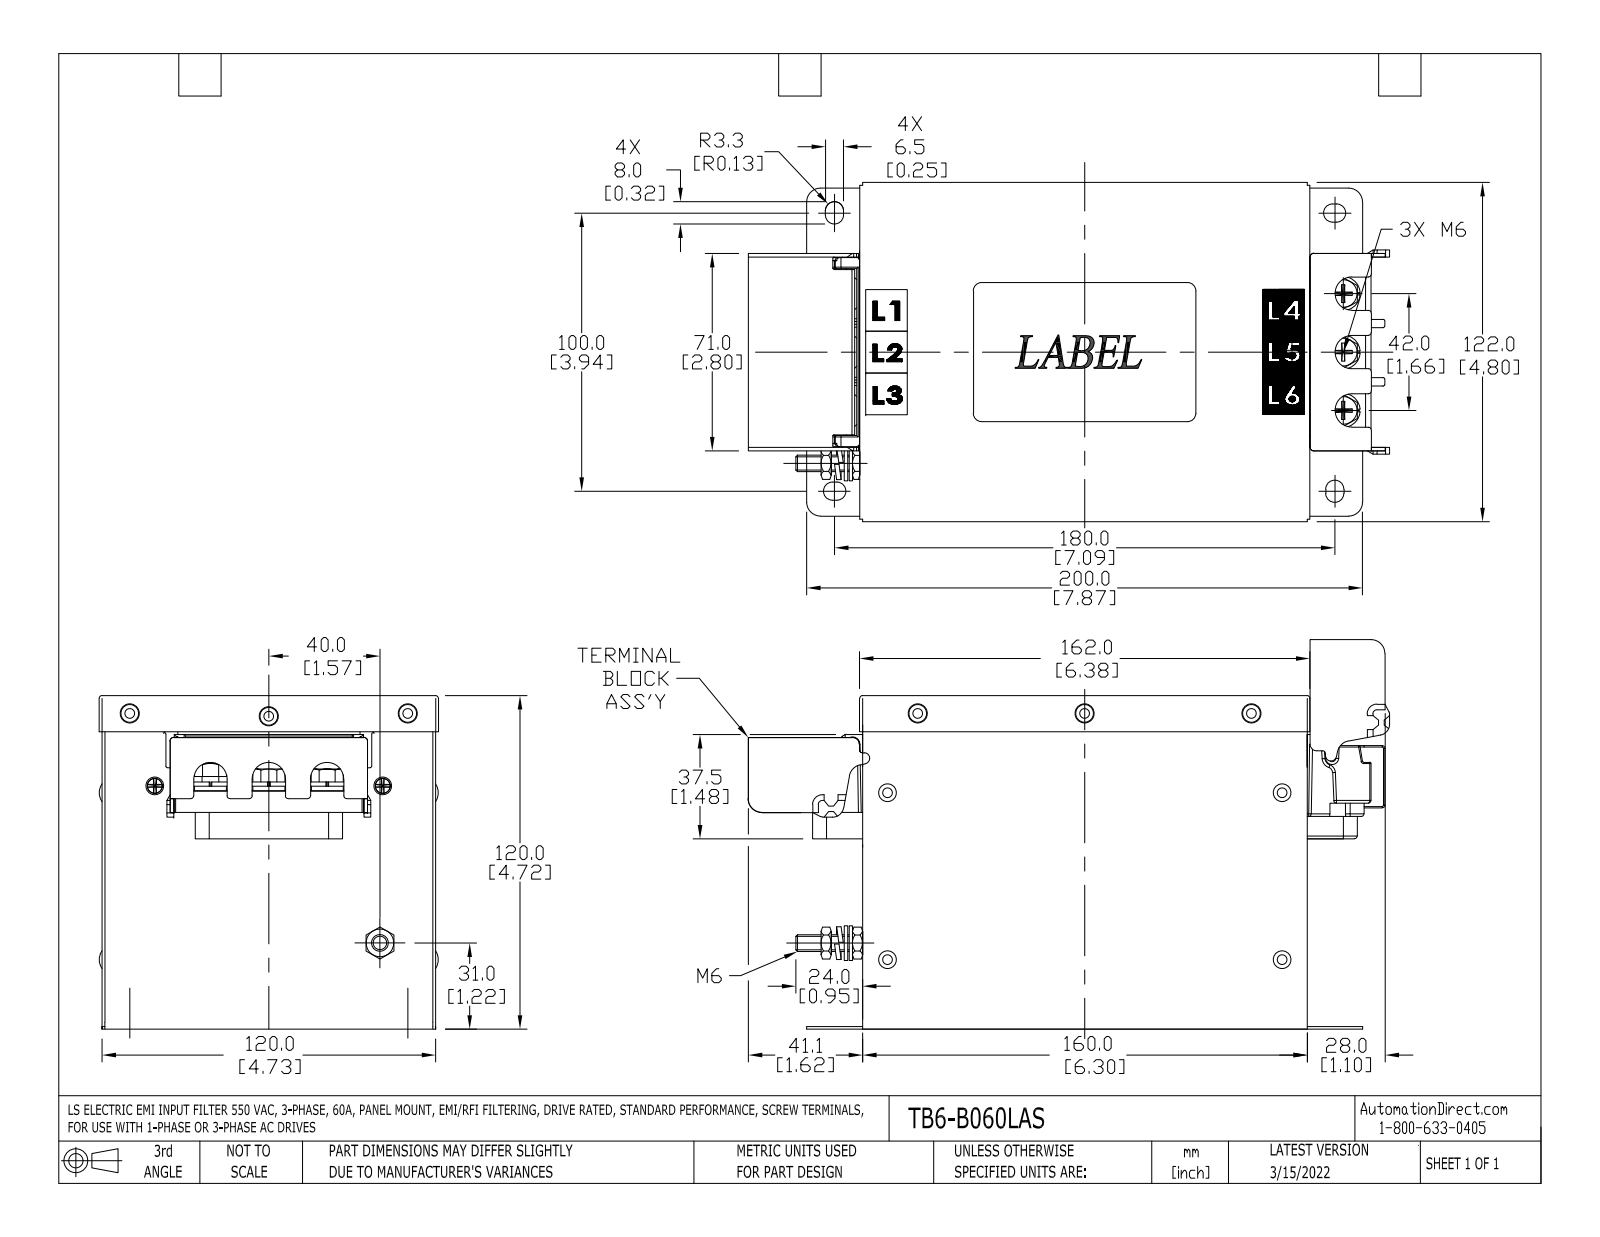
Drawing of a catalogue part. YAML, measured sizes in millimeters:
part_name: "TB6-B060AS"
step_written_by: "SolidWorks 2021 (AUTOMOTIVE_DESIGN)"
units: millimeters
bodies: {solids: 50, faces: 1921, planar: 871, cylindrical: 568, other: 482}
overall_size: [230.8, 131, 124]
volume: 439200
surface_area: 278600
round_holes:
  - {diameter: 2, count: 13}
  - {diameter: 3.3, count: 11}
  - {diameter: 3.5, count: 10}
  - {diameter: 7.3, count: 6}
  - {diameter: 3.9, count: 1}
  - {diameter: 4.2, count: 1}
  - {diameter: 5, count: 1}
  - {diameter: 5.2, count: 1}
round_bosses_or_shafts:
  - {diameter: 3.5, count: 13}
  - {diameter: 12.2, count: 6}
  - {diameter: 11.5, count: 6}
  - {diameter: 6.4, count: 4}
  - {diameter: 1.4, count: 2}
  - {diameter: 10, count: 1}
  - {diameter: 6.7, count: 1}
  - {diameter: 5.9, count: 1}
partial_cylinders:
  - {radius: 0.5, count: 167}
  - {radius: 1, count: 13}
  - {radius: 2, count: 12}
  - {radius: 1.7, count: 7}
  - {radius: 0.3, count: 6}
  - {radius: 0.7, count: 3}
  - {radius: 1.9, count: 3}
  - {radius: 7, count: 2}
face_to_face_distances: [1.2, 118.8, 120, 158.8, 107, 105.8, 13, 1, 117.6, 160]
hole_center_spacings: [10, 64.3, 147.6, 147.9, 150, 163.2, 126, 189.7]
